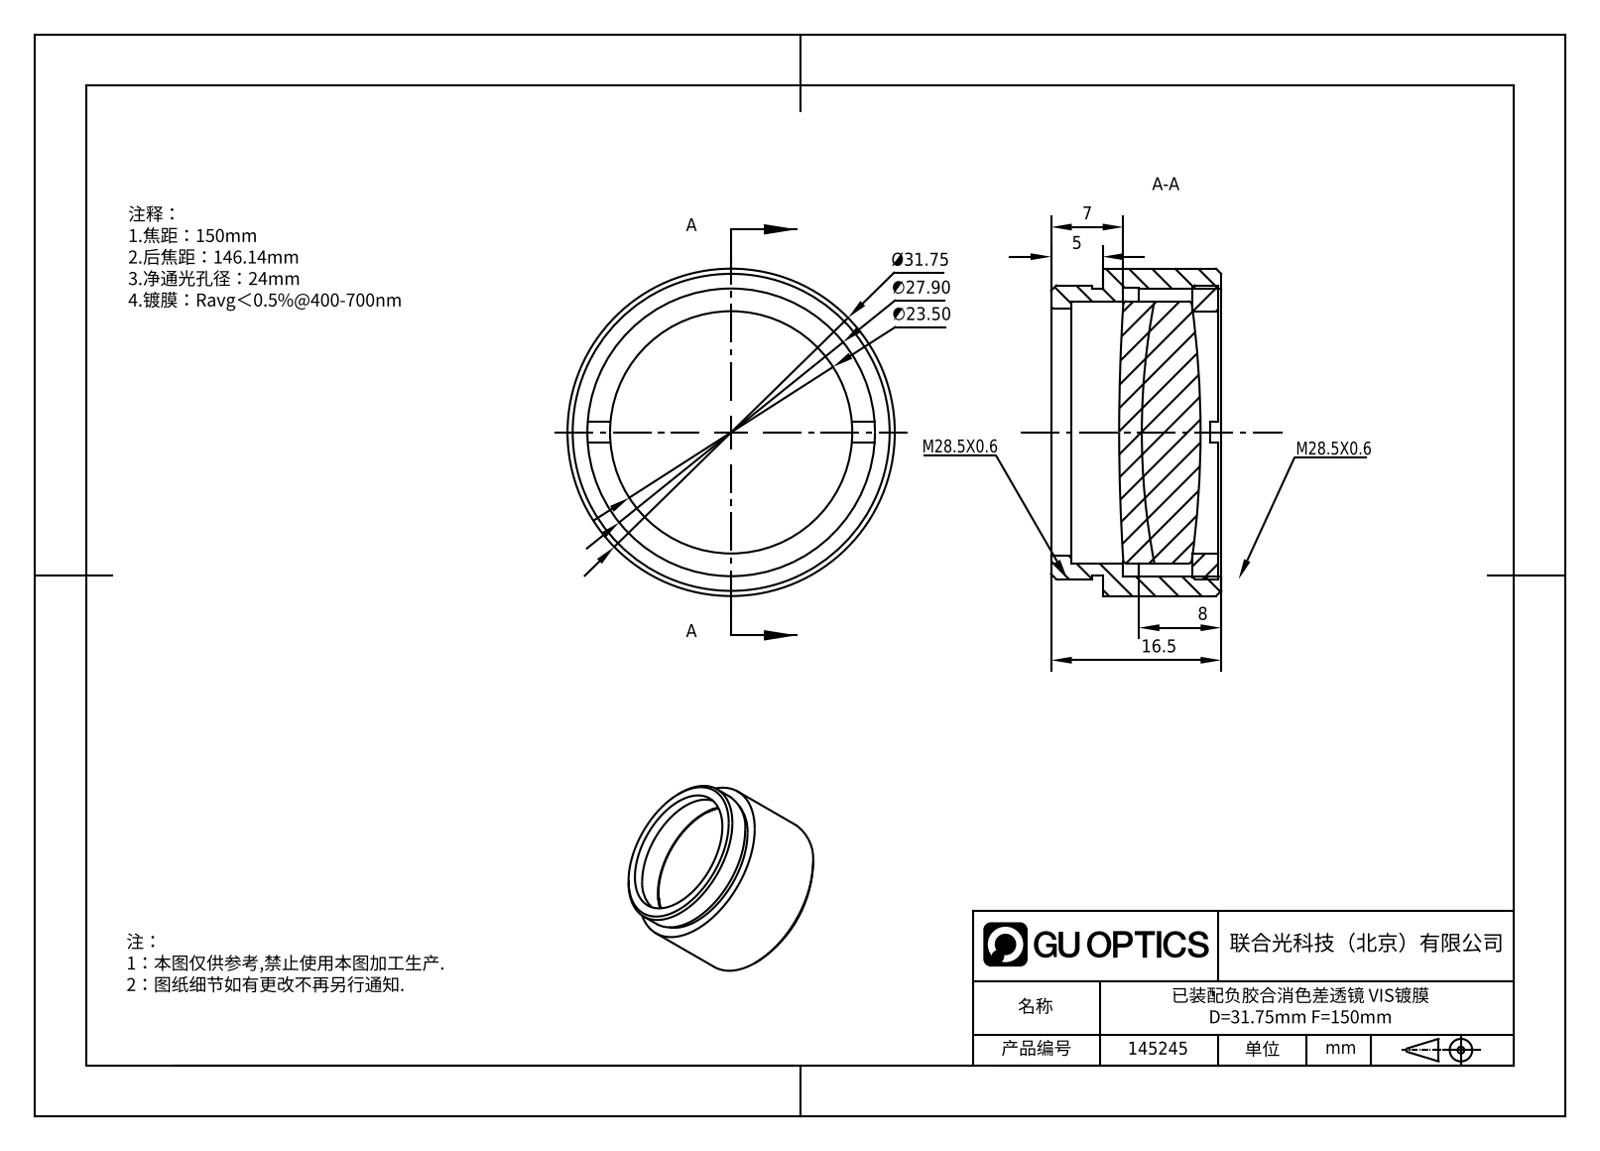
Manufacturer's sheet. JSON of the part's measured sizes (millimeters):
{"part_name": "M28.5x0.6ѹȦ; GL31-025B-150-VIS_Solidworks; APD-ML25-150-VIS; M28.5x0.6安装环PN35020-LM254-D1", "step_written_by": "SolidWorks 2022 (AUTOMOTIVE_DESIGN)", "units": "millimeters", "bodies": {"solids": 4, "faces": 56, "planar": 16, "cylindrical": 22, "other": 18}, "overall_size": [31.76, 31.76, 16.5], "volume_mm3": 7162, "surface_area_mm2": 7028, "round_holes": [[23.5, 1], [24, 1], [27.9, 1], [28, 1]], "round_bosses_or_shafts": [[31.76, 1], [28.5, 1], [27.8, 1], [25.4, 1]], "face_to_face_distances": [2, 5, 2.5, 8.74, 11.24, 13.74, 16.24, 16.5, 11.5, 2.76]}
